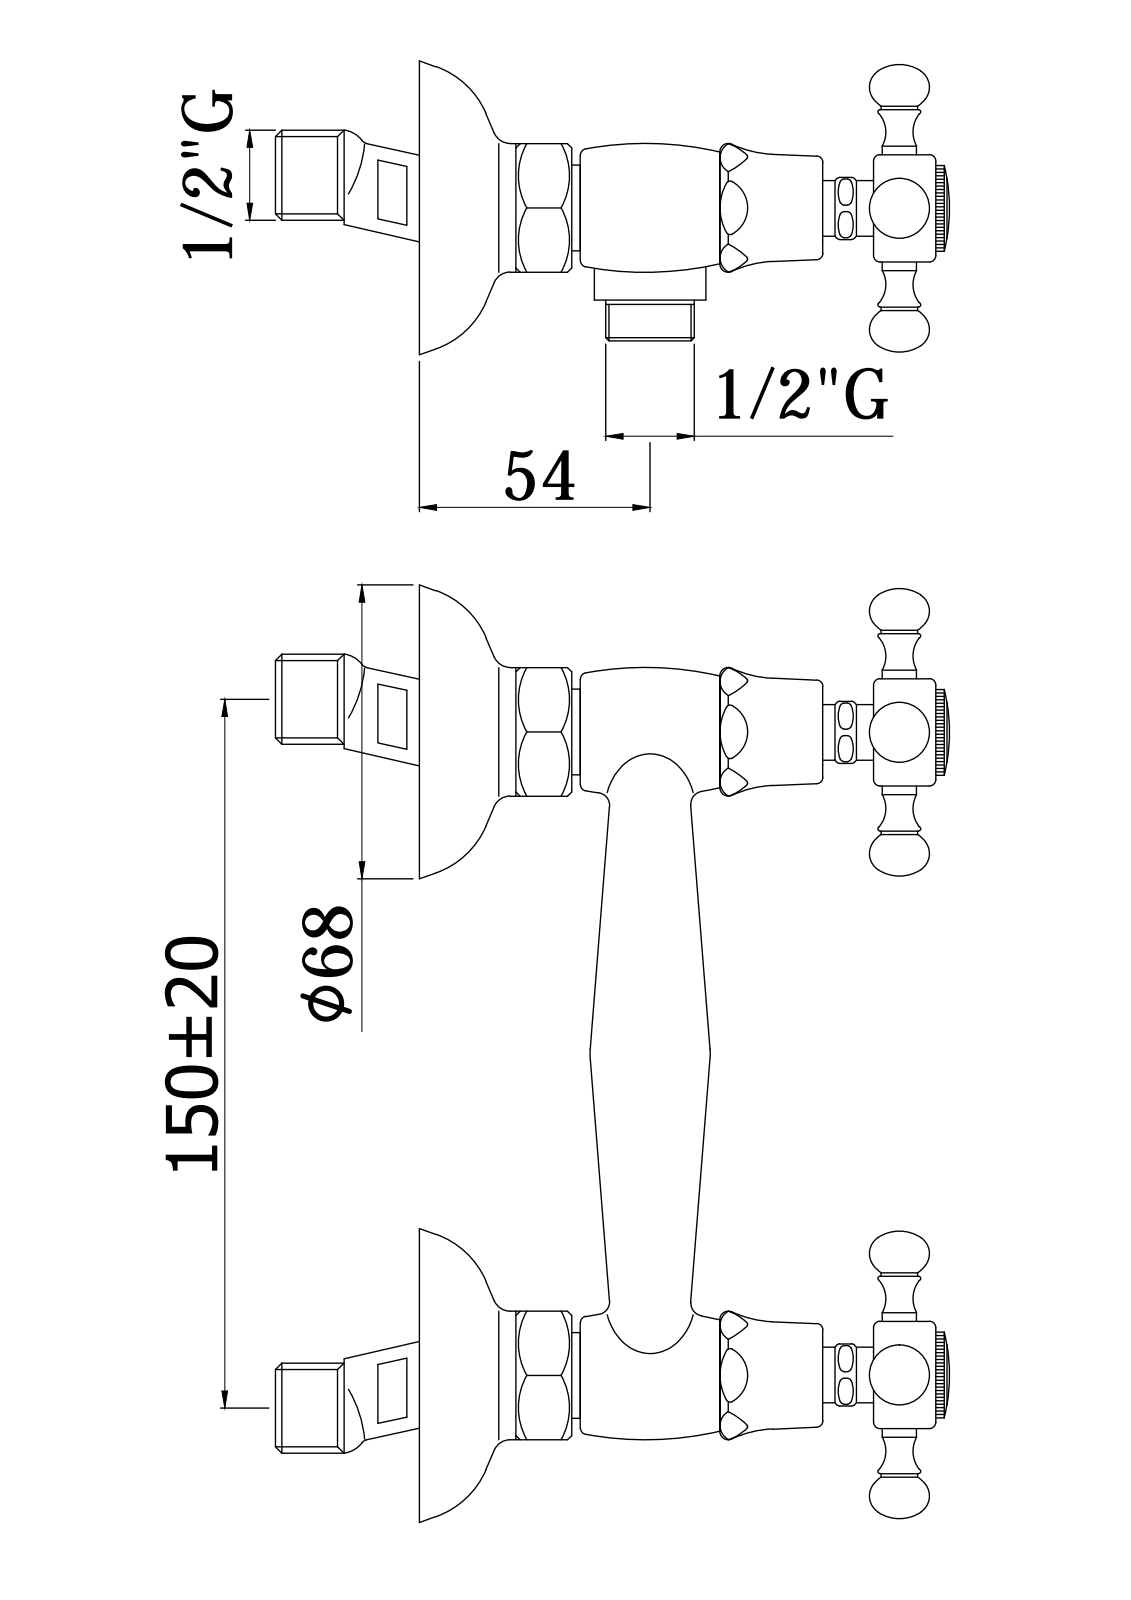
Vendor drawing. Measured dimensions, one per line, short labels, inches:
name: FBLV168CR
written by: CREO PARAMETRIC BY PTC INC, 2020044 (CONFIG_CONTROL_DESIGN)
unit: in
bodies: 3 solids, 1095 faces (501 planar, 322 cylindrical, 272 other)
size: 8.661 × 4.87 × 2.756
volume: 8.576 in³; area: 120.4 in²
holes: 2× ⌀0.65, 2× ⌀0.732, 2× ⌀0.748, 2× ⌀0.846, 2× ⌀0.984, 2× ⌀2.677, 1× ⌀0.594, 1× ⌀0.827, 1× ⌀0.945
bosses: 3× ⌀0.354, 3× ⌀0.276, 2× ⌀2.756, 2× ⌀1.108, 2× ⌀0.551, 2× ⌀0.512, 1× ⌀1.094, 1× ⌀0.984
rounds: 2× R0.433, 1× R0.207
face distances: 0.689, 1.996, 1.307, 3.386, 0.709, 2.697, 1.39, 0.276, 0.984, 0.02
hole spacings: 5.906
